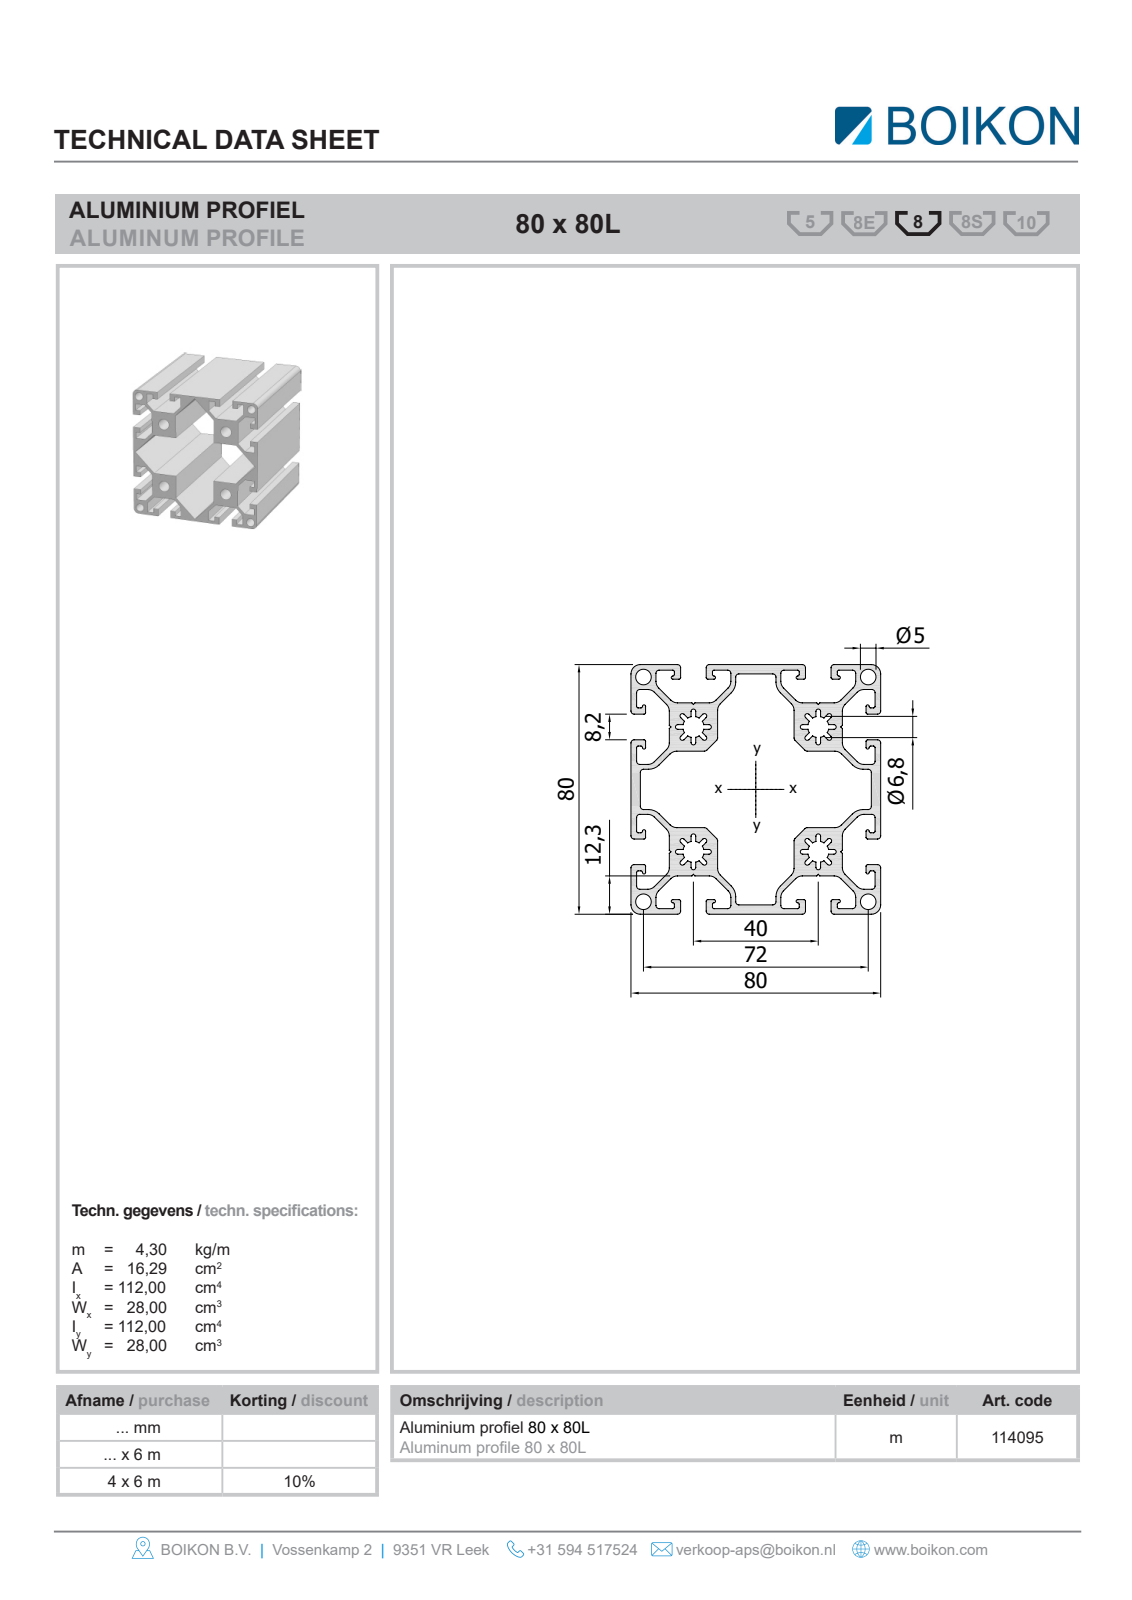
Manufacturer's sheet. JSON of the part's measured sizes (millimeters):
{"part_name": "Root; 11409580x80LBOIKON0", "step_written_by": "HiCAD 2013 1802.4 Build 509 (AUTOMOTIVE_DESIGN)", "units": "millimeters", "bodies": {"solids": 1, "faces": 146, "planar": 134, "cylindrical": 12, "other": 0}, "overall_size": [1000, 80, 80], "volume_mm3": 1899000, "surface_area_mm2": 1180000, "round_holes": [[5, 4], [6.8, 4]], "partial_cylinders_radius": [[3, 4]], "face_to_face_distances": [40, 1.8, 80, 27.7, 52.3, 28.28, 12.3, 67.7, 15.4, 4.5], "hole_center_spacings": [58.24, 22.63, 40, 72, 79.2, 56.57, 101.82]}
